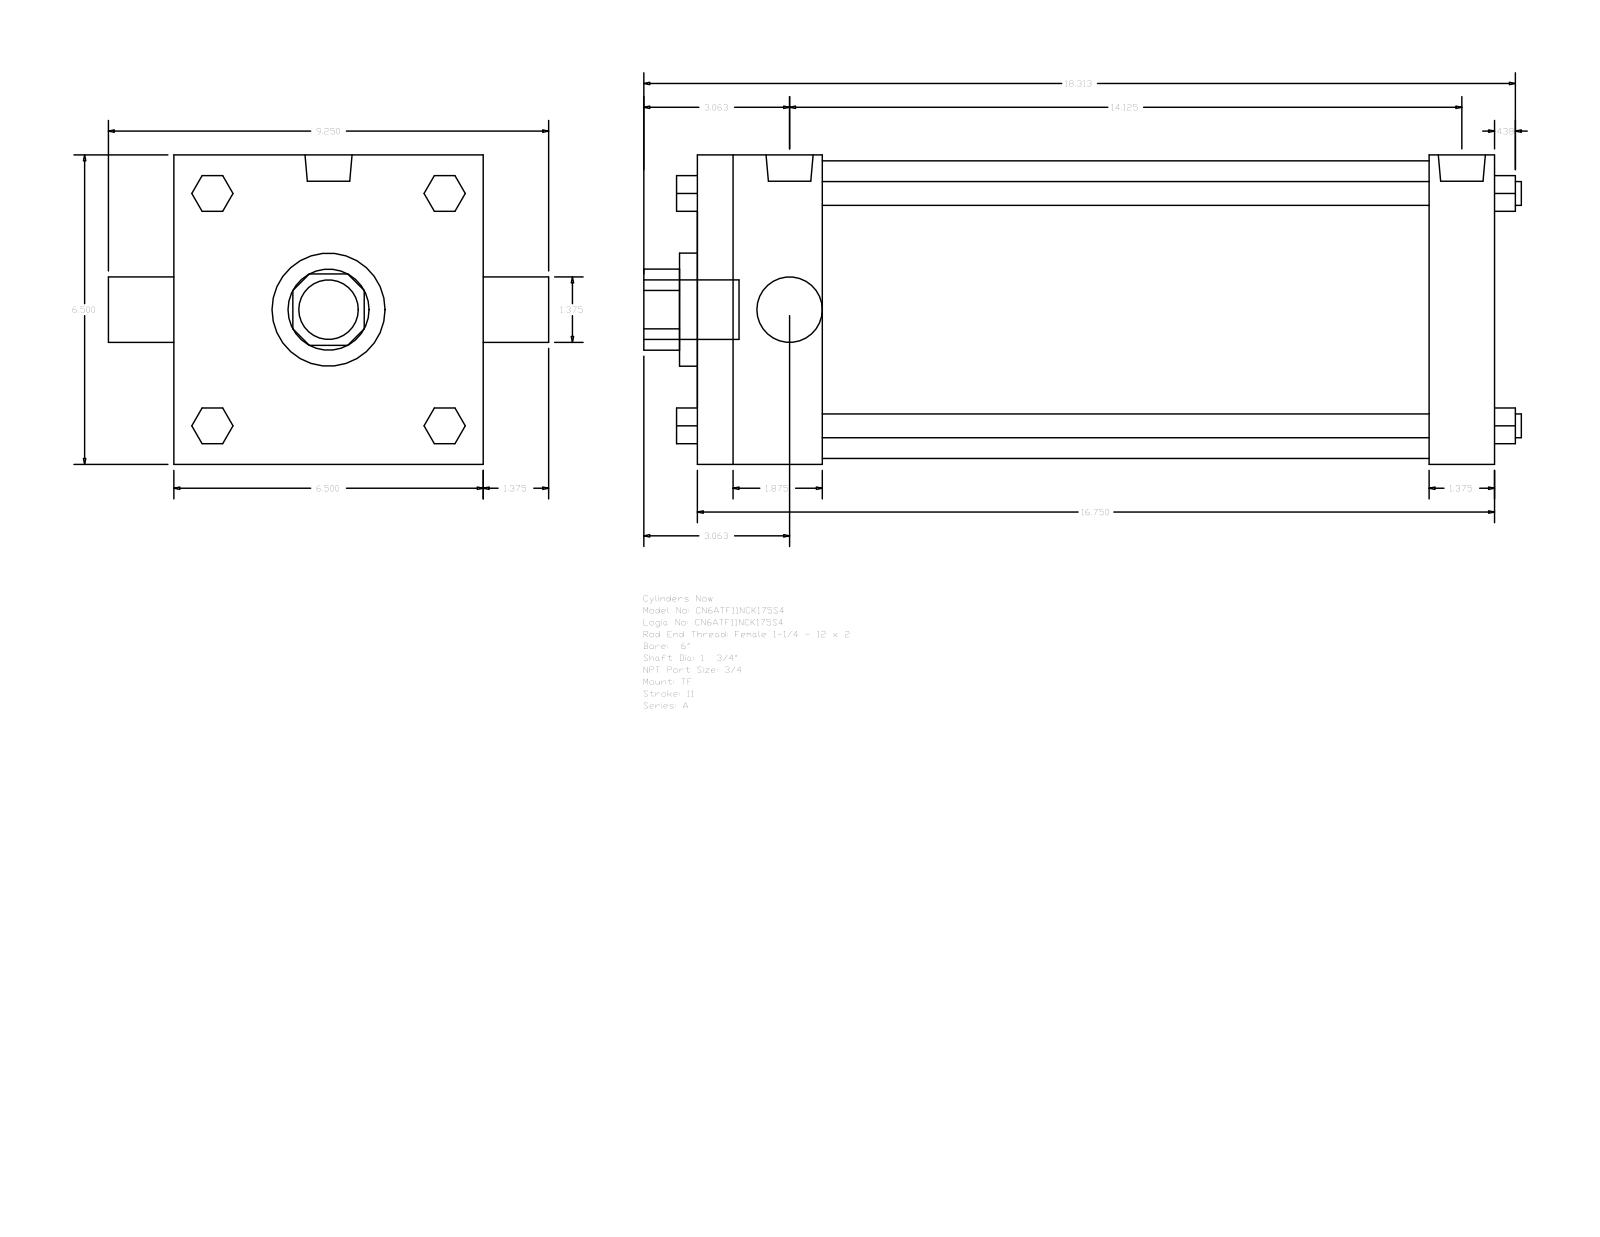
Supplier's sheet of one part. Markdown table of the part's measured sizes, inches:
| quantity | value |
| --- | --- |
| part name | A_TF__0600_1.75 |
| STEP written by | GSSL Pune (CONFIG_CONTROL_DESIGN) |
| units | inches |
| bodies | 0 solids, 120 faces (92 planar, 28 cylindrical, 0 other) |
| overall size | 18.437 × 9.25 × 6.5 |
| round holes (diameter × count) | 1.375 × 1, 1.75 × 1, 2.375 × 1, 6.25 × 1 |
| round bosses / shafts (diameter × count) | 0.5 × 4, 0.594 × 3, 0.989 × 2, 1.25 × 1 |
| partial cylindrical surfaces (radius × count) | 0.852 × 1 |
| main face-to-face distances | 6.5, 16.75, 1.375, 2.625, 14.125, 15.375, 12.75, 0.75, 2.44, 4.226 |
